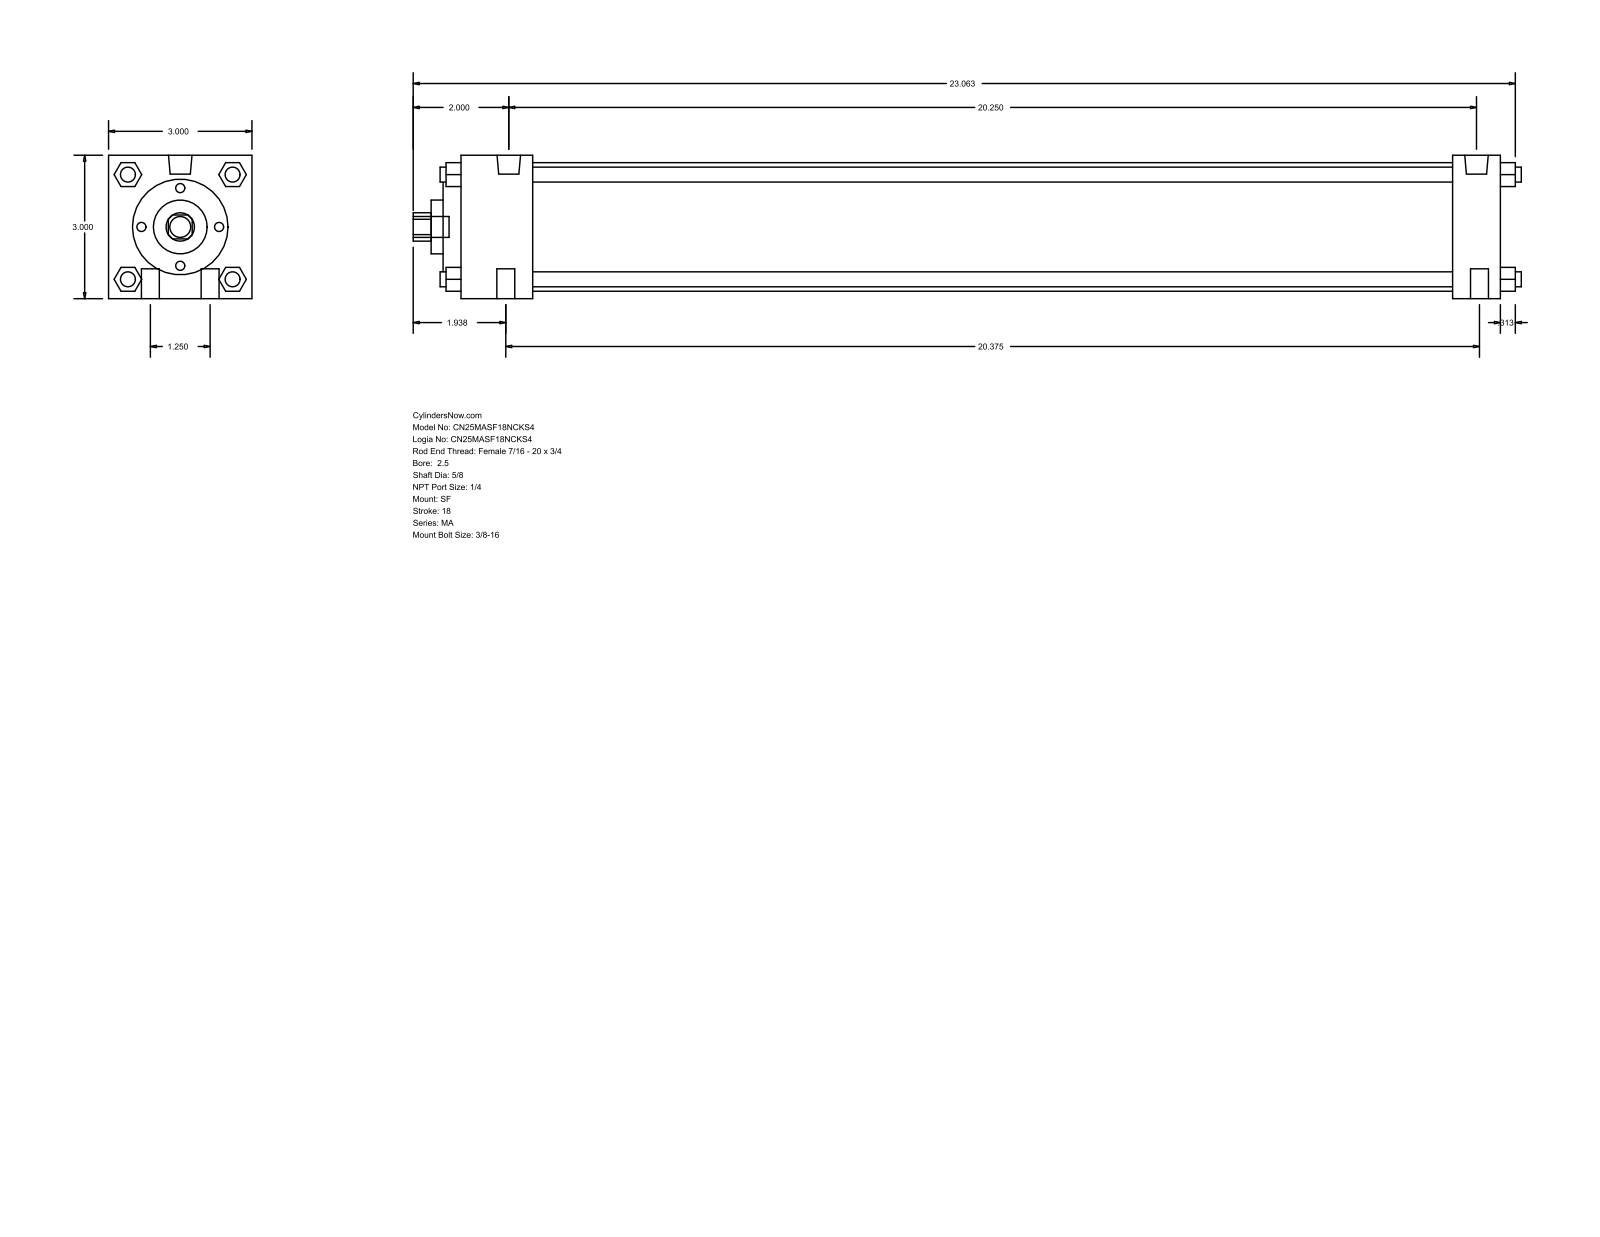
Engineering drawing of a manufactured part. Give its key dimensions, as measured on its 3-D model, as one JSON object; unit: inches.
{"part_name": "MA_SF__0250_0.625", "step_written_by": "GSSL Pune (CONFIG_CONTROL_DESIGN)", "units": "inches", "bodies": {"solids": 0, "faces": 126, "planar": 95, "cylindrical": 31, "other": 0}, "overall_size": [23.187, 3, 3], "round_holes": [[0.625, 1], [1.125, 1], [2, 1], [2.69, 1]], "round_bosses_or_shafts": [[0.313, 6], [0.375, 4], [0.492, 2], [0.437, 1]], "partial_cylinders_radius": [[0.297, 1]], "face_to_face_distances": [3, 21.75, 1, 20.75, 1.5, 19.25, 20.25, 0.5, 0.375, 1.875]}
